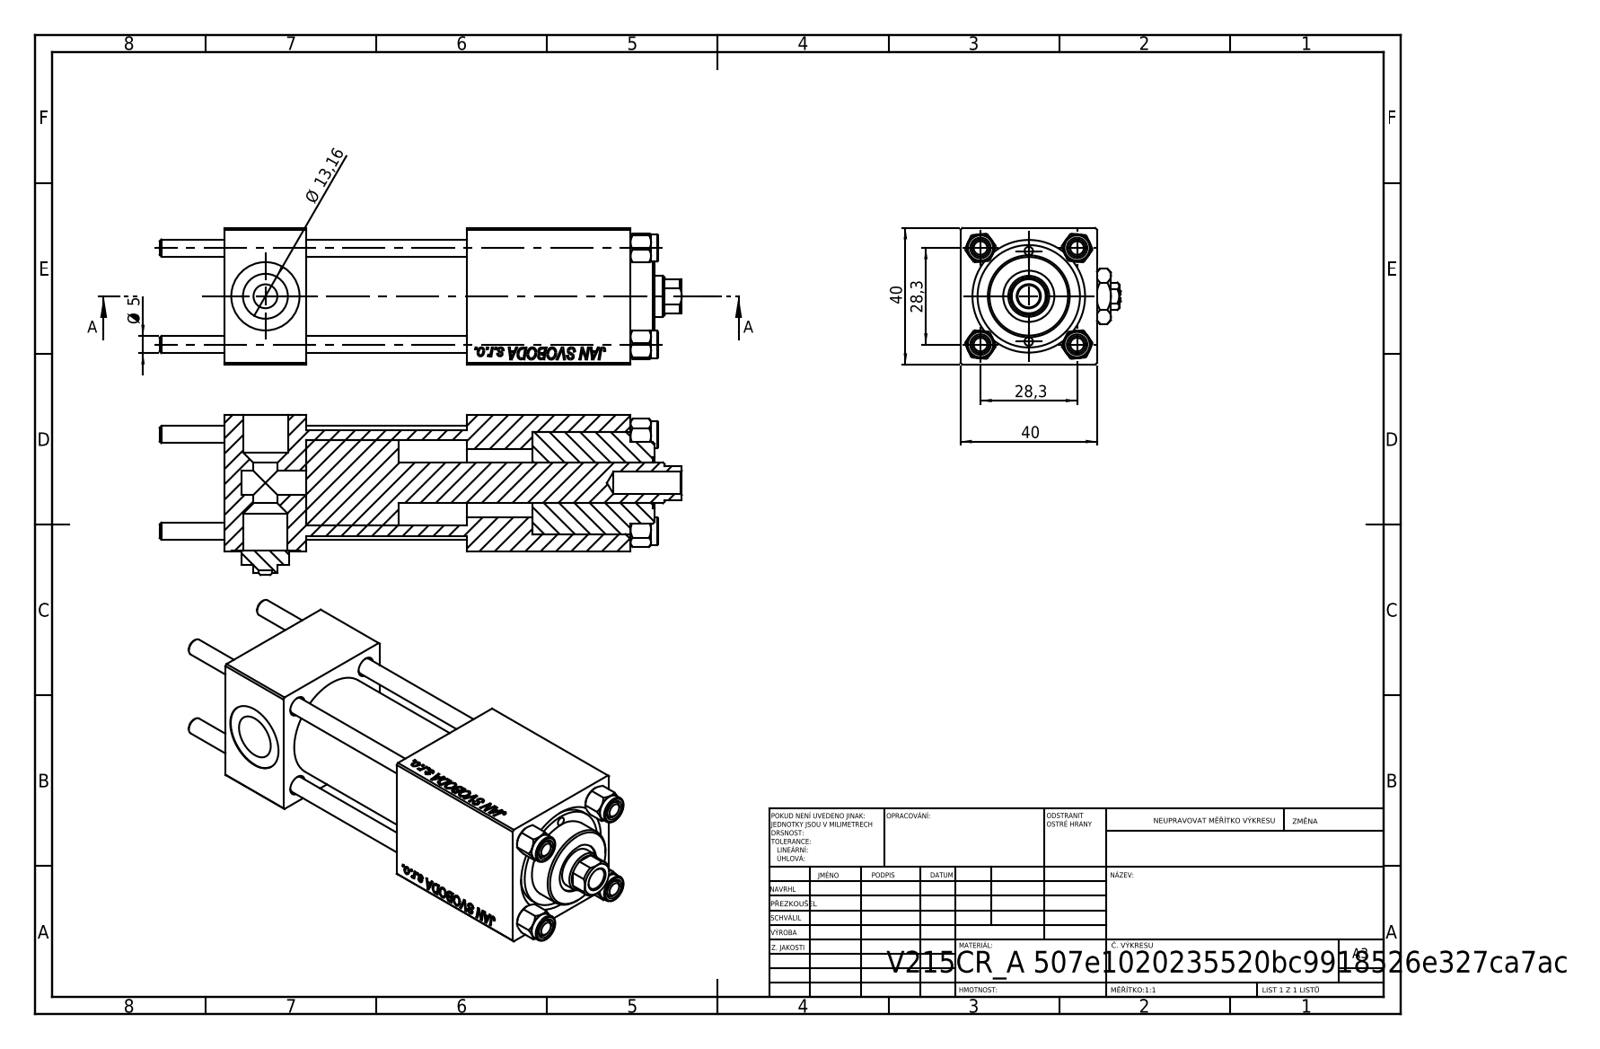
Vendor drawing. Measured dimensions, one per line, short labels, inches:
name: V215CR_VCP; NUT_M5; V215CR_BODY_A; V215_VC_A (+2 more)
written by: SolidWorks 2019 (CONFIG_CONTROL_DESIGN)
unit: in
bodies: 12 solids, 1190 faces (542 planar, 90 cylindrical, 558 other)
size: 6.024 × 1.85 × 1.575
volume: 8.766 in³; area: 93.06 in²
holes: 4× ⌀0.197, 3× ⌀0.787, 2× ⌀0.098, 2× ⌀0.276, 2× ⌀0.518, 1× ⌀0.256, 1× ⌀0.472, 1× ⌀0.512, 1× ⌀0.591, 1× ⌀0.984, 1× ⌀1.181
bosses: 4× ⌀0.315, 1× ⌀1.22, 1× ⌀0.945
rounds: 1× R0.217
face distances: 1.575, 0.945, 3.74, 3.555, 2.61, 4.685, 1.13, 0.76, 1.85, 2.795
hole spacings: 0.558, 0.788, 1.114, 1.214, 0.522, 1.576, 1.043
